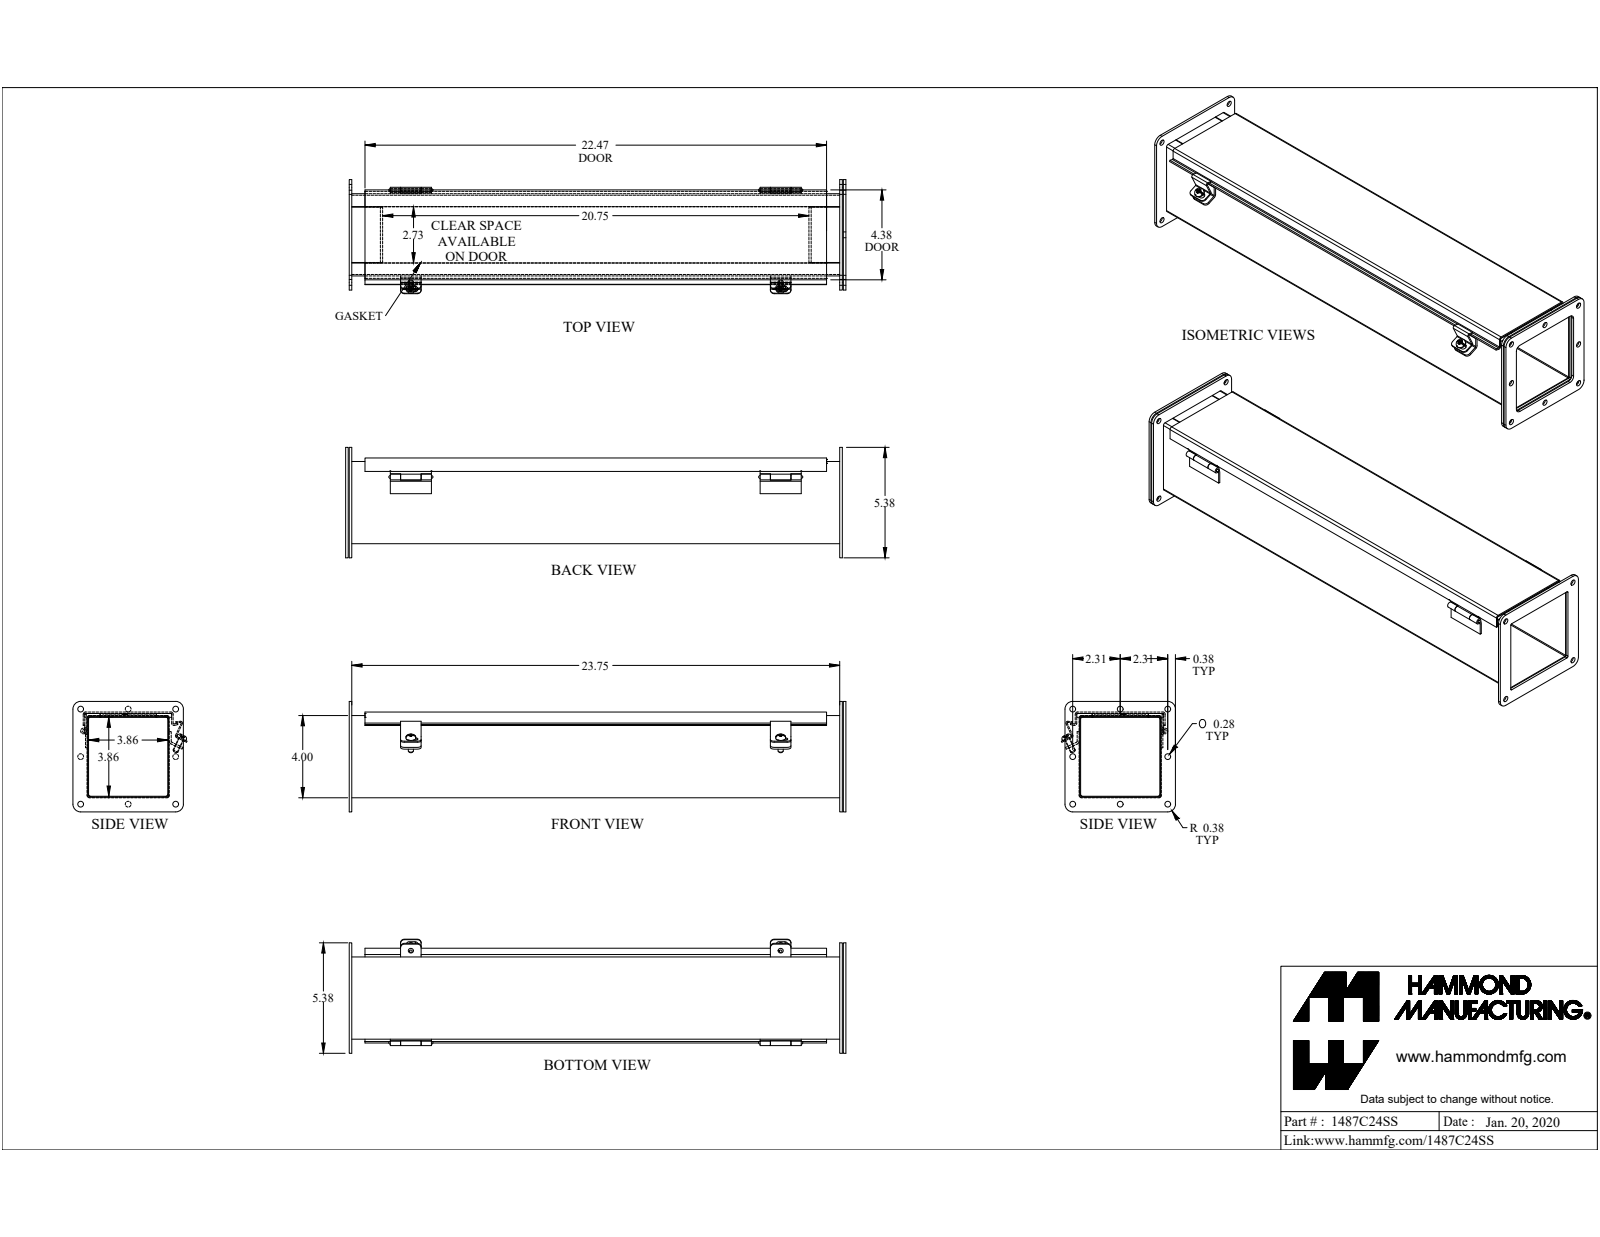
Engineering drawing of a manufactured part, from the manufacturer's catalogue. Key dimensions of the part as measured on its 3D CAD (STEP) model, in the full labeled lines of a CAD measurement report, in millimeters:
Part name (STEP PRODUCT): 1487C24SS
STEP written by: SolidWorks 2019 (CONFIG_CONTROL_DESIGN)
Units: millimetres
Bodies: 27 solids, 546 faces (350 planar, 144 cylindrical, 52 other)
Overall size (bounding box): 623.5 × 141 × 136.5
Volume: 742 300 mm³ · Surface area: 734 800 mm²
Round holes (diameter × count): ⌀7.1 ×8, ⌀5.4 ×2, ⌀4.7 ×1, ⌀5 ×1, ⌀6.6 ×1, ⌀8.9 ×1
Round bosses / shafts (diameter × count): ⌀6.4 ×3, ⌀12.2 ×2, ⌀12.7 ×1, ⌀8.6 ×1, ⌀4.6 ×1
Partial cylindrical surfaces — rounded edges, fillets, slot ends (radius × count): R4.8 ×8, R9.5 ×8, R0.9 ×7, R2.7 ×7, R0.5 ×6, R0.8 ×4, R1.6 ×4, R3.6 ×4
Main face-to-face distances: 1.8, 99.8, 104.1, 101.6, 97.9, 106, 102.3, 4.7, 4.4, 6.6
Hole centre spacings: 58.8, 131.3, 117.5, 117.5, 58.7, 83.1, 83.1, 131.3
